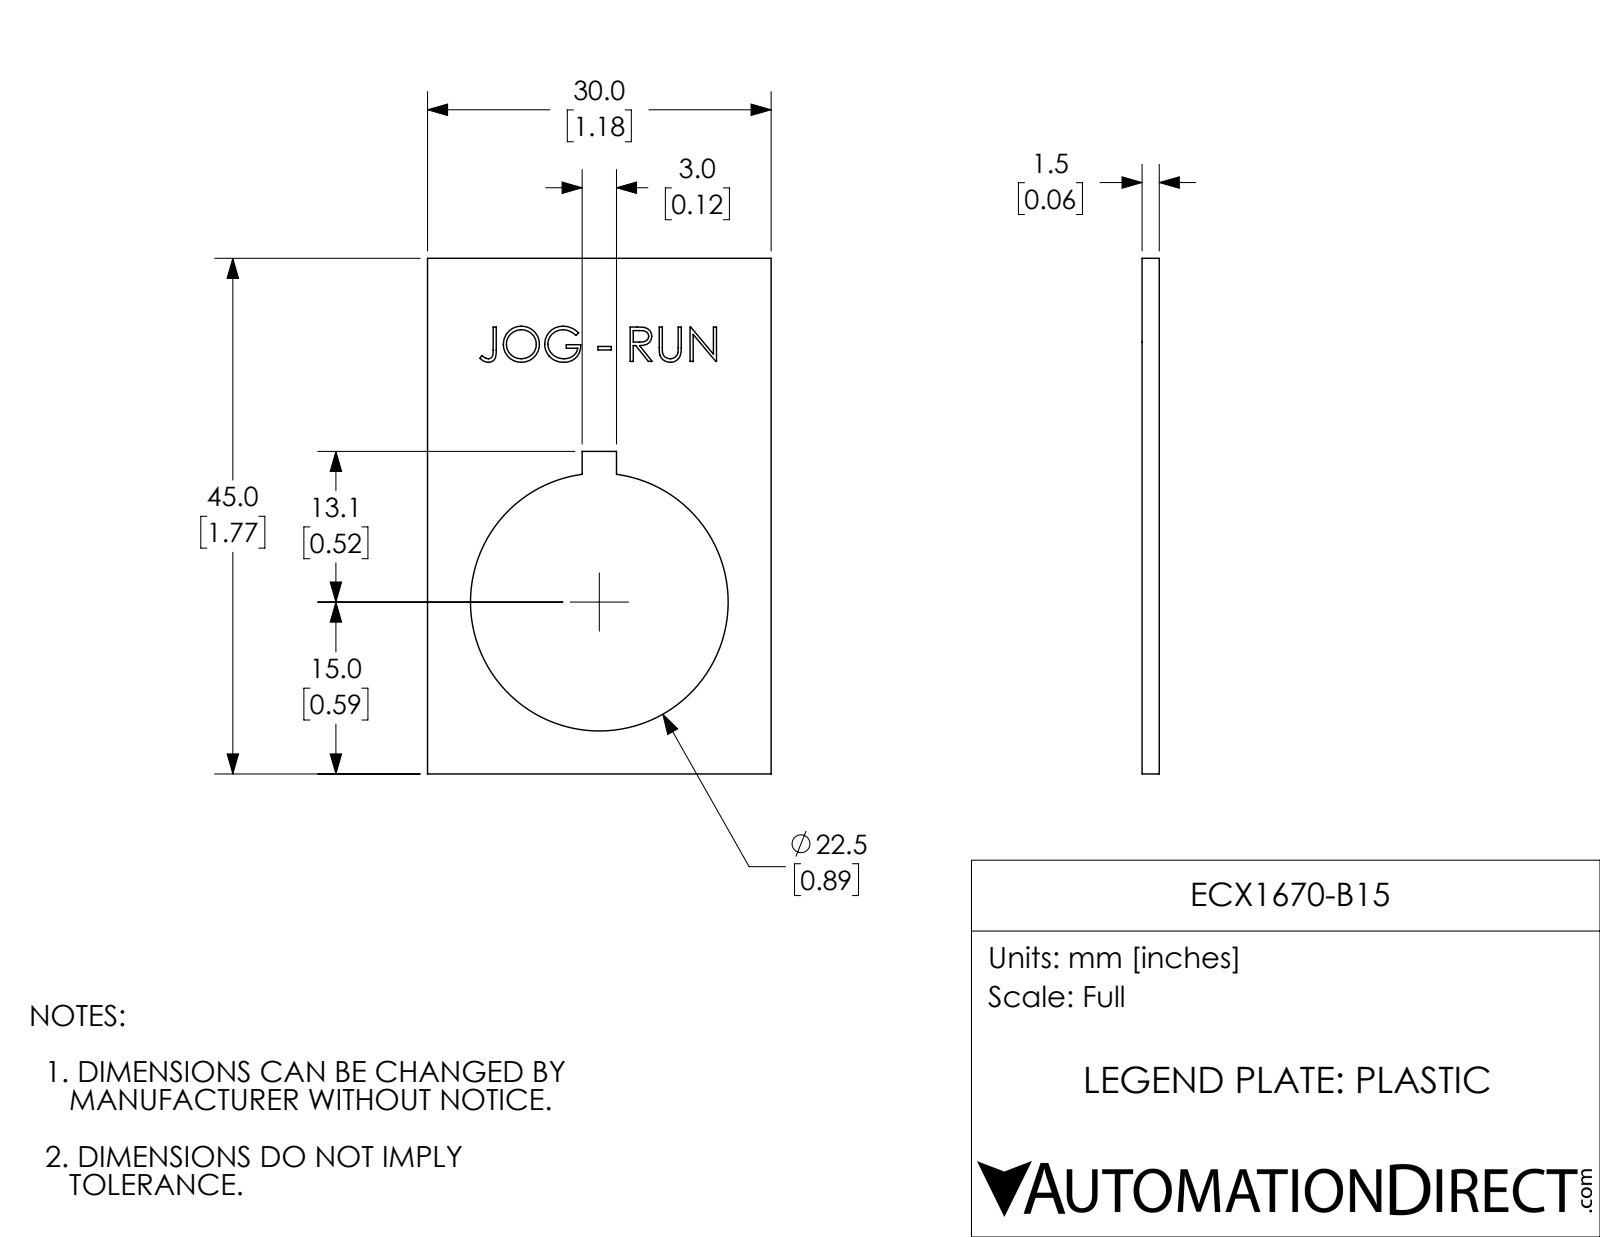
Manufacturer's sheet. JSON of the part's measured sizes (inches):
{"part_name": "ECX1670-B15", "step_written_by": "SolidWorks 2017 (AUTOMOTIVE_DESIGN)", "units": "inches", "bodies": {"solids": 1, "faces": 94, "planar": 57, "cylindrical": 3, "other": 34}, "overall_size": [1.772, 1.181, 0.059], "volume_in3": 0.087, "surface_area_in2": 3.461, "round_holes": [[0.886, 1]], "face_to_face_distances": [0.059, 1.181, 1.772, 0.058, 0.531, 0.65, 1.108, 0.663, 0.118, 0.165]}
